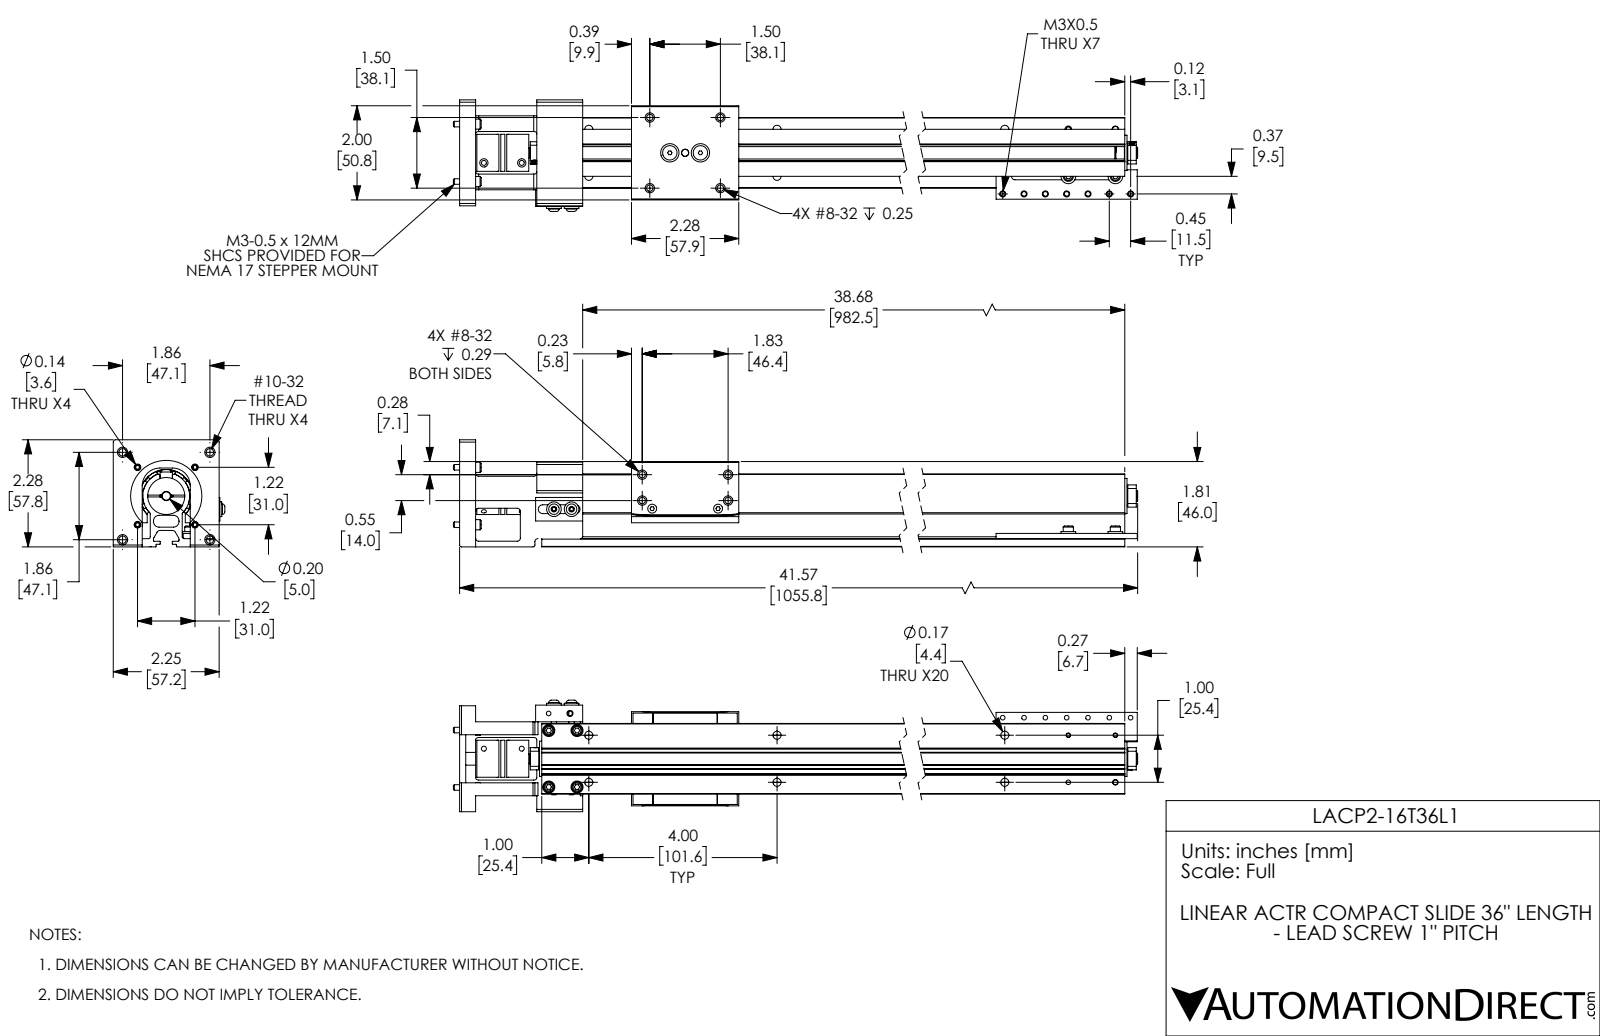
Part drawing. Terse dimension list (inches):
name: LACP2-16T36L1; LACP2-16T36L1_BLOCK; LACP2-16T36L1_BODY
written by: SolidWorks 2017 (AUTOMOTIVE_DESIGN)
unit: in
bodies: 46 solids, 1264 faces (502 planar, 493 cylindrical, 269 other)
size: 41.7 × 2.37 × 2.275
volume: 37.32 in³; area: 566.1 in²
holes: 20× ⌀0.172, 18× ⌀0.098, 10× ⌀0.136, 4× ⌀0.141, 4× ⌀0.147, 4× ⌀0.159, 4× ⌀0.257, 2× ⌀0.099, 2× ⌀0.106, 2× ⌀0.118, 2× ⌀0.125, 2× ⌀0.125
bosses: 10× ⌀0.217, 10× ⌀0.118, 4× ⌀0.312, 3× ⌀0.118, 2× ⌀0.307, 2× ⌀0.224, 2× ⌀0.164, 2× ⌀0.138
rounds: 17× R0.01, 9× R0.05, 8× R0.039, 7× R0.065, 4× R0.02, 4× R0.074, 4× R0.079, 4× R0.118
face distances: 0.175, 0.679, 0.411, 1.089, 0.67, 0.495, 0.419, 0.244, 0.251, 0.175
hole spacings: 1, 4, 4.123, 16, 16.031, 8, 8, 8.062
